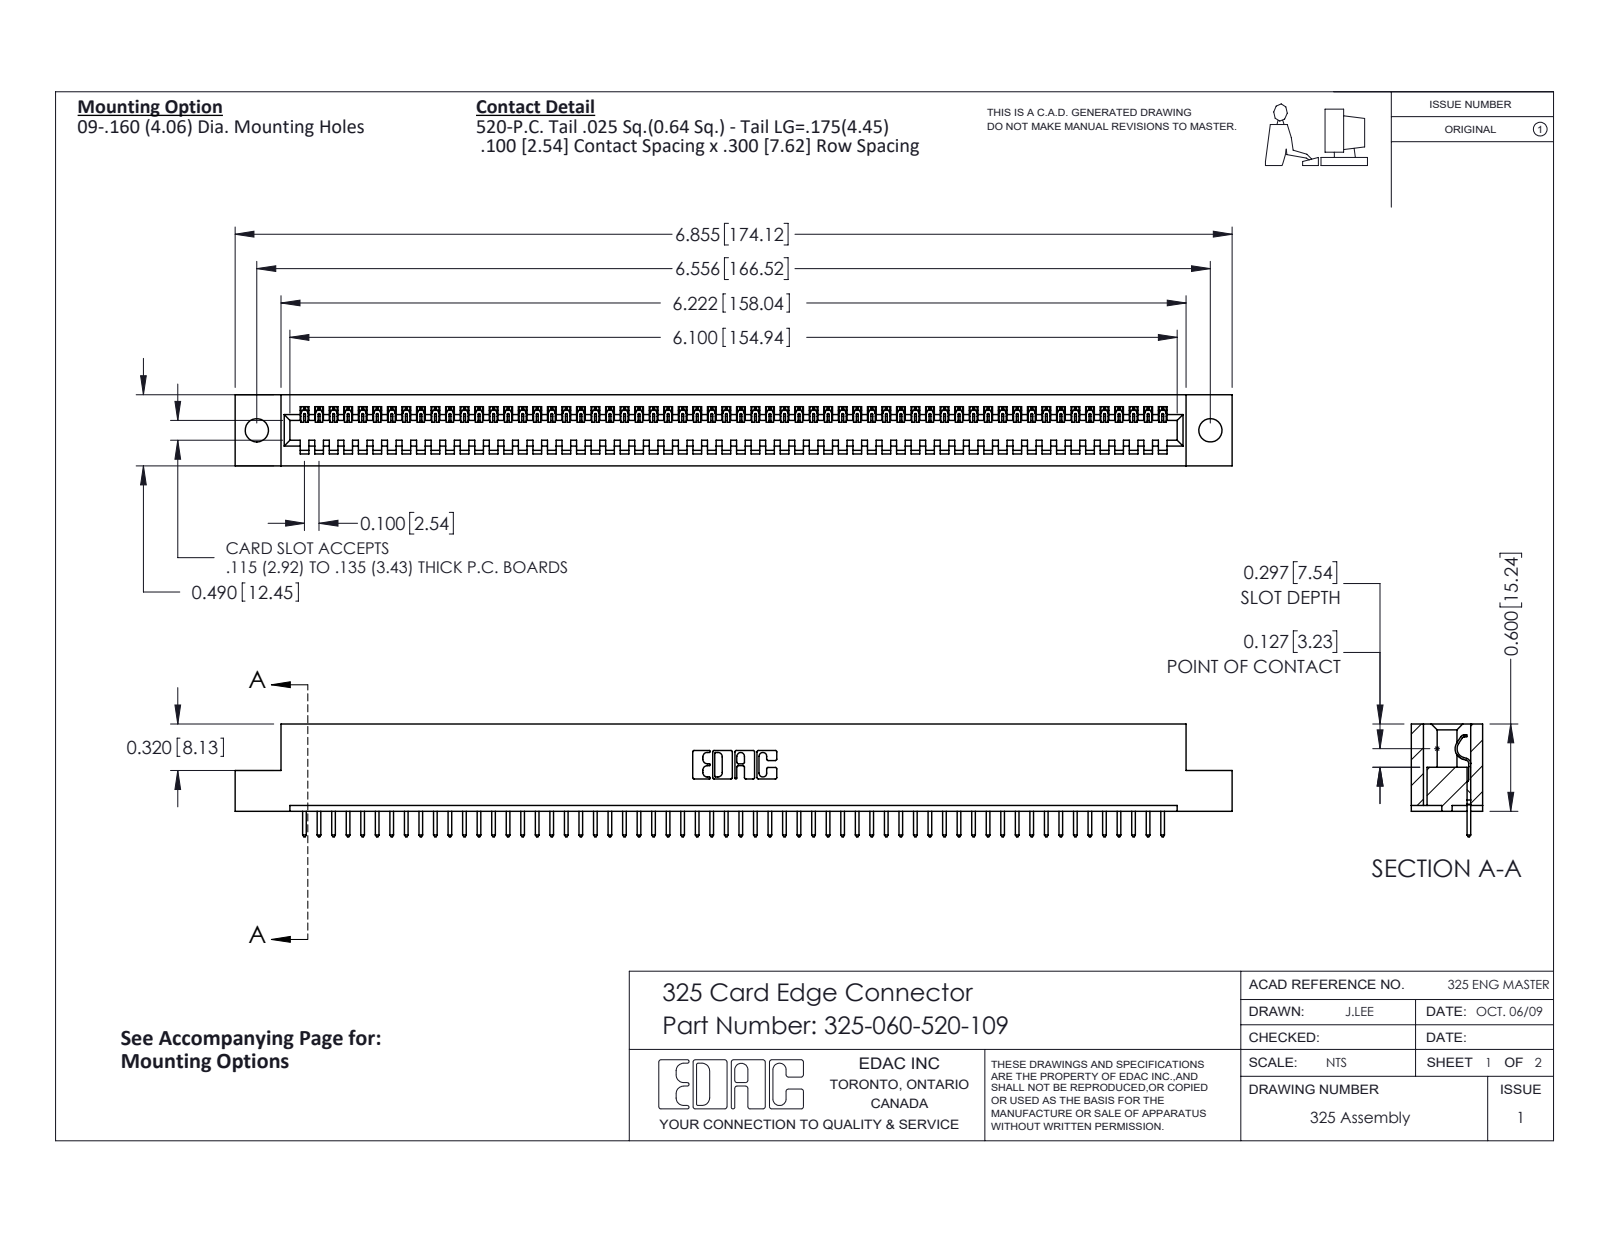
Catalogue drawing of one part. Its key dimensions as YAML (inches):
part_name: "325-060-520-109; 325-292-001_325-293-120; 325 Part_.160 TH"
step_written_by: "SolidWorks 2016 (CONFIG_CONTROL_DESIGN)"
units: inches
bodies: {solids: 61, faces: 3594, planar: 2590, cylindrical: 1004, other: 0}
overall_size: [6.855, 0.775, 0.49]
volume: 1.334
surface_area: 36.35
round_holes:
  - {diameter: 0.16, count: 2}
partial_cylinders:
  - {radius: 0.006, count: 120}
  - {radius: 0.01, count: 120}
  - {radius: 0.01, count: 22}
  - {radius: 0.007, count: 6}
  - {radius: 0.031, count: 6}
  - {radius: 0.026, count: 3}
  - {radius: 0.014, count: 1}
  - {radius: 0.022, count: 1}
face_to_face_distances: [0.083, 0.407, 0.49, 0.3, 0.107, 0.383, 0.025, 0.325, 0.56, 0.263]
hole_center_spacings: [6.556]
